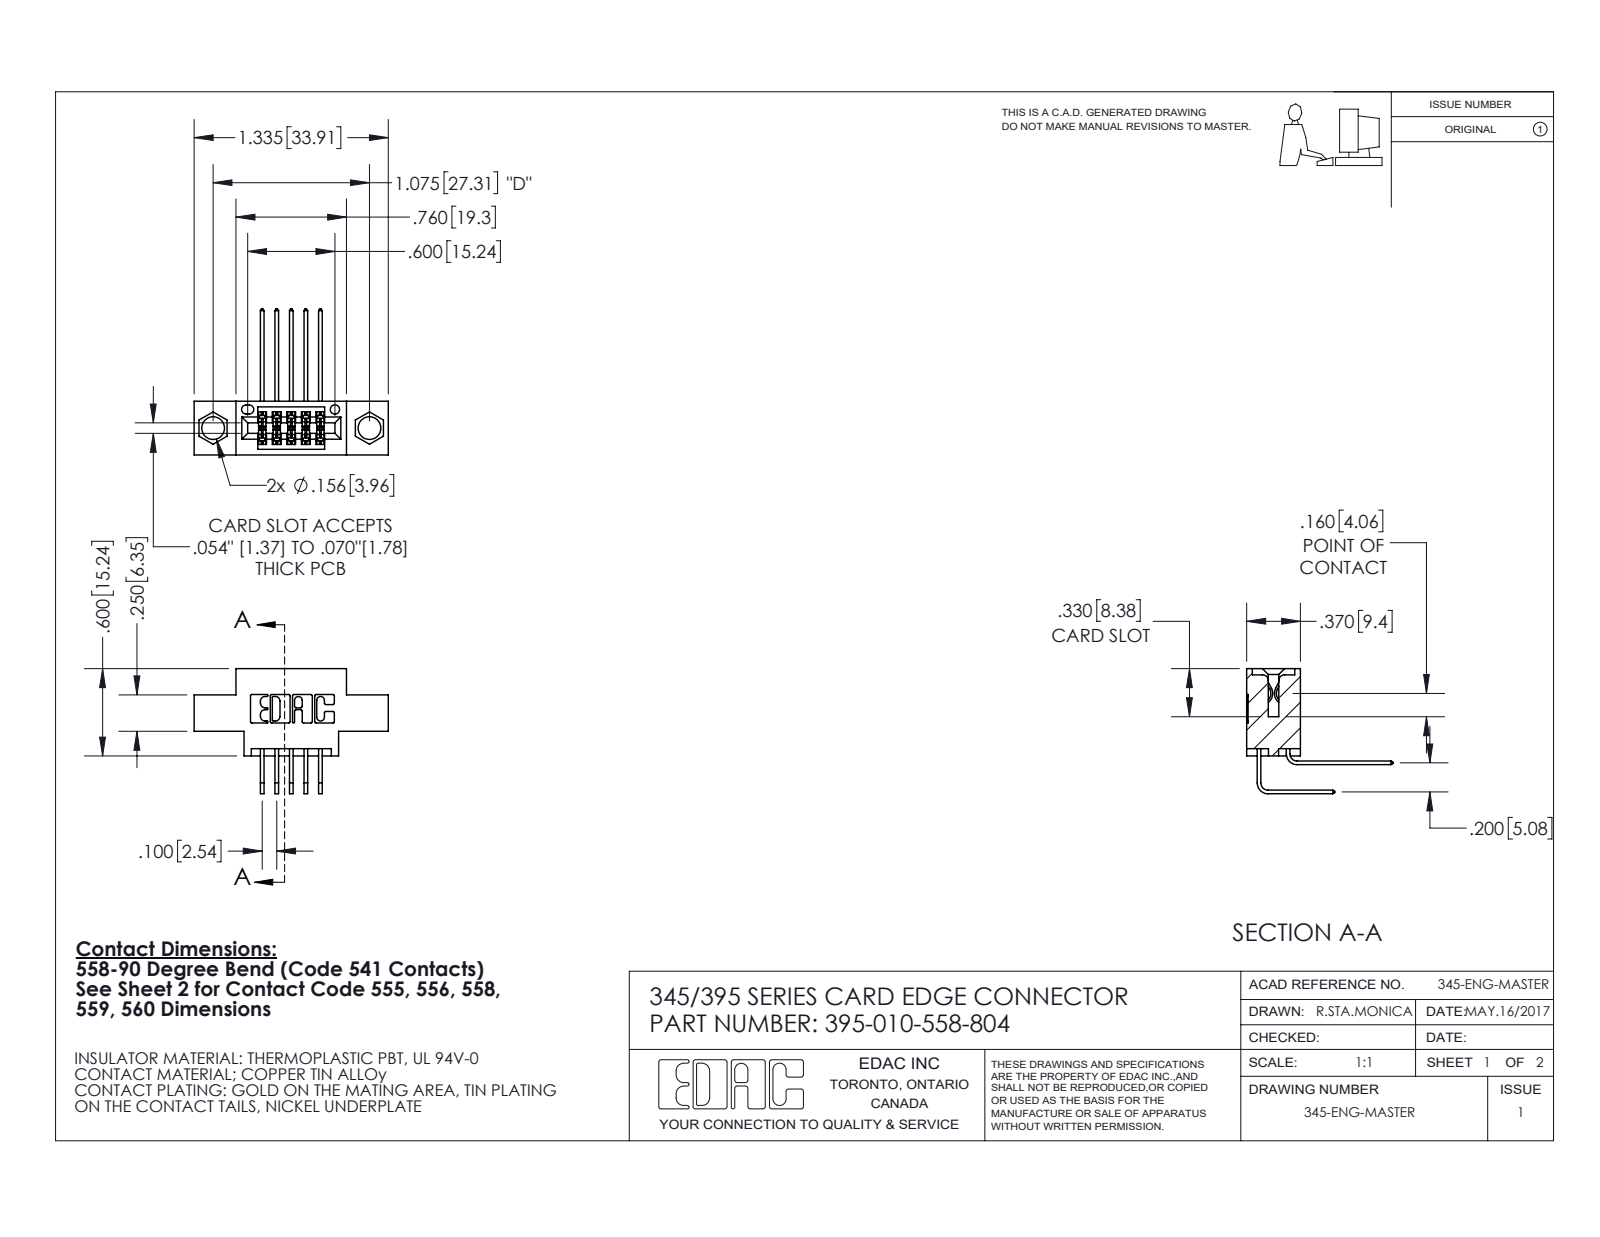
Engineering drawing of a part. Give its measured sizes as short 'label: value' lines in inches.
name: 345 Part_0.170 Offset - 0.156 Dia-TI; 345-292-001_558 559 Tail - 1; 395-010-558-804; 345-292-001_558 Tail - 2
written by: SolidWorks 2020 (CONFIG_CONTROL_DESIGN)
unit: in
bodies: 11 solids, 664 faces (448 planar, 216 cylindrical, 0 other)
size: 1.335 × 1.005 × 0.859
volume: 0.17 in³; area: 5.692 in²
holes: 2× ⌀0.156, 1× ⌀0.064
rounds: 22× R0.01, 15× R0.006, 6× R0.007, 6× R0.031, 3× R0.026, 2× R0.014, 2× R0.019, 2× R0.022
face distances: 0.2, 0.37, 0.1, 0.072, 0.298, 0.098, 0.272, 0.025, 0.25, 0.06
hole spacings: 0.27, 0.847, 1.075
